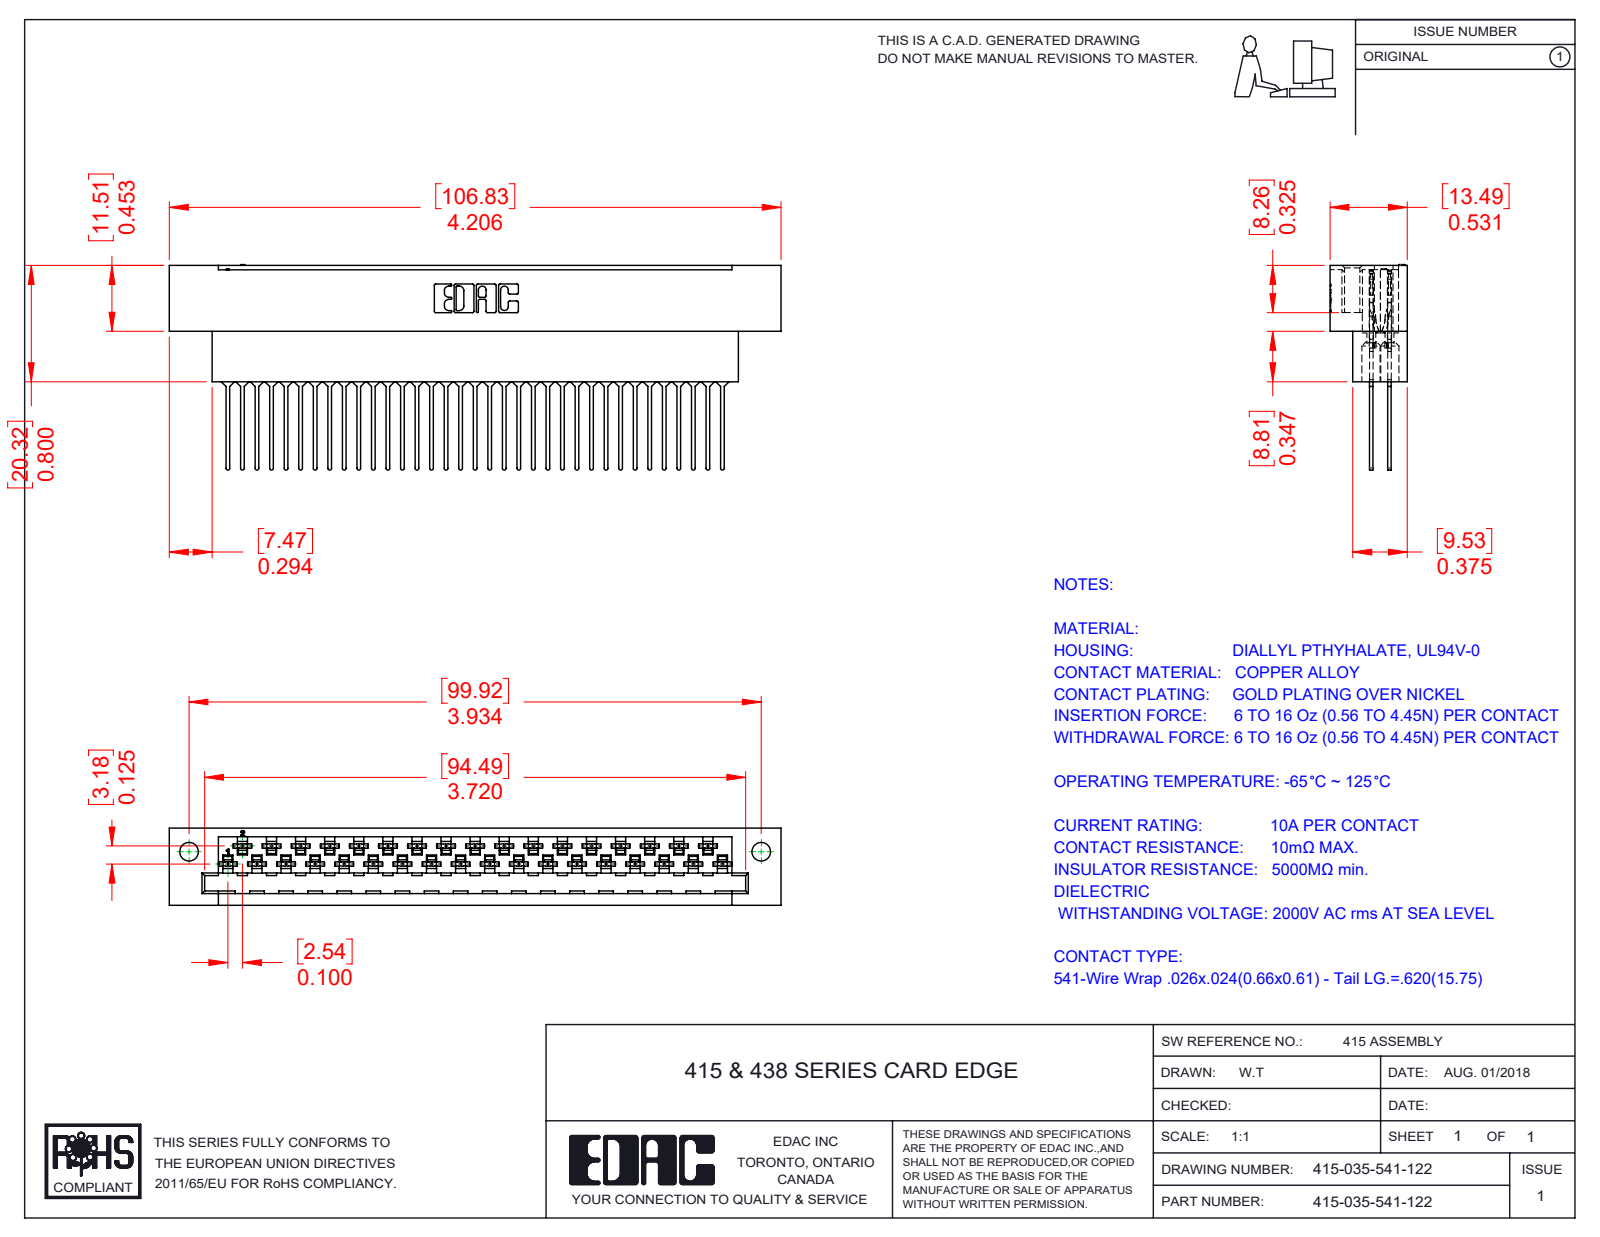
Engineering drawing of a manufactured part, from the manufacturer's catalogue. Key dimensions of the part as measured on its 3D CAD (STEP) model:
Part name (STEP PRODUCT): 415-035-541-122; 516-290-001_541; 415-210-001_415-210-035-122
STEP written by: SolidWorks 2016 (CONFIG_CONTROL_DESIGN)
Units: millimetres
Bodies: 36 solids, 3574 faces (2283 planar, 954 cylindrical, 337 other)
Overall size (bounding box): 106.83 × 35.85 × 13.49
Volume: 17 574 mm³ · Surface area: 23 097 mm²
Round holes (diameter × count): ⌀1.27 ×35, ⌀3.3 ×35, ⌀3.25 ×2
Partial cylindrical surfaces — rounded edges, fillets, slot ends (radius × count): R0.3 ×140, R0.56 ×140, R0.18 ×70, R0.2 ×70, R0.41 ×70, R2.03 ×70, R0.33 ×35, R0.25 ×22
Main face-to-face distances: 3.18, 0.61, 7.49, 1.27, 1.88, 13.49, 6.61, 6.88, 6, 2.82
Hole centre spacings: 5.08, 10.16, 15.24, 20.32, 25.4, 30.48, 35.56, 2.54
